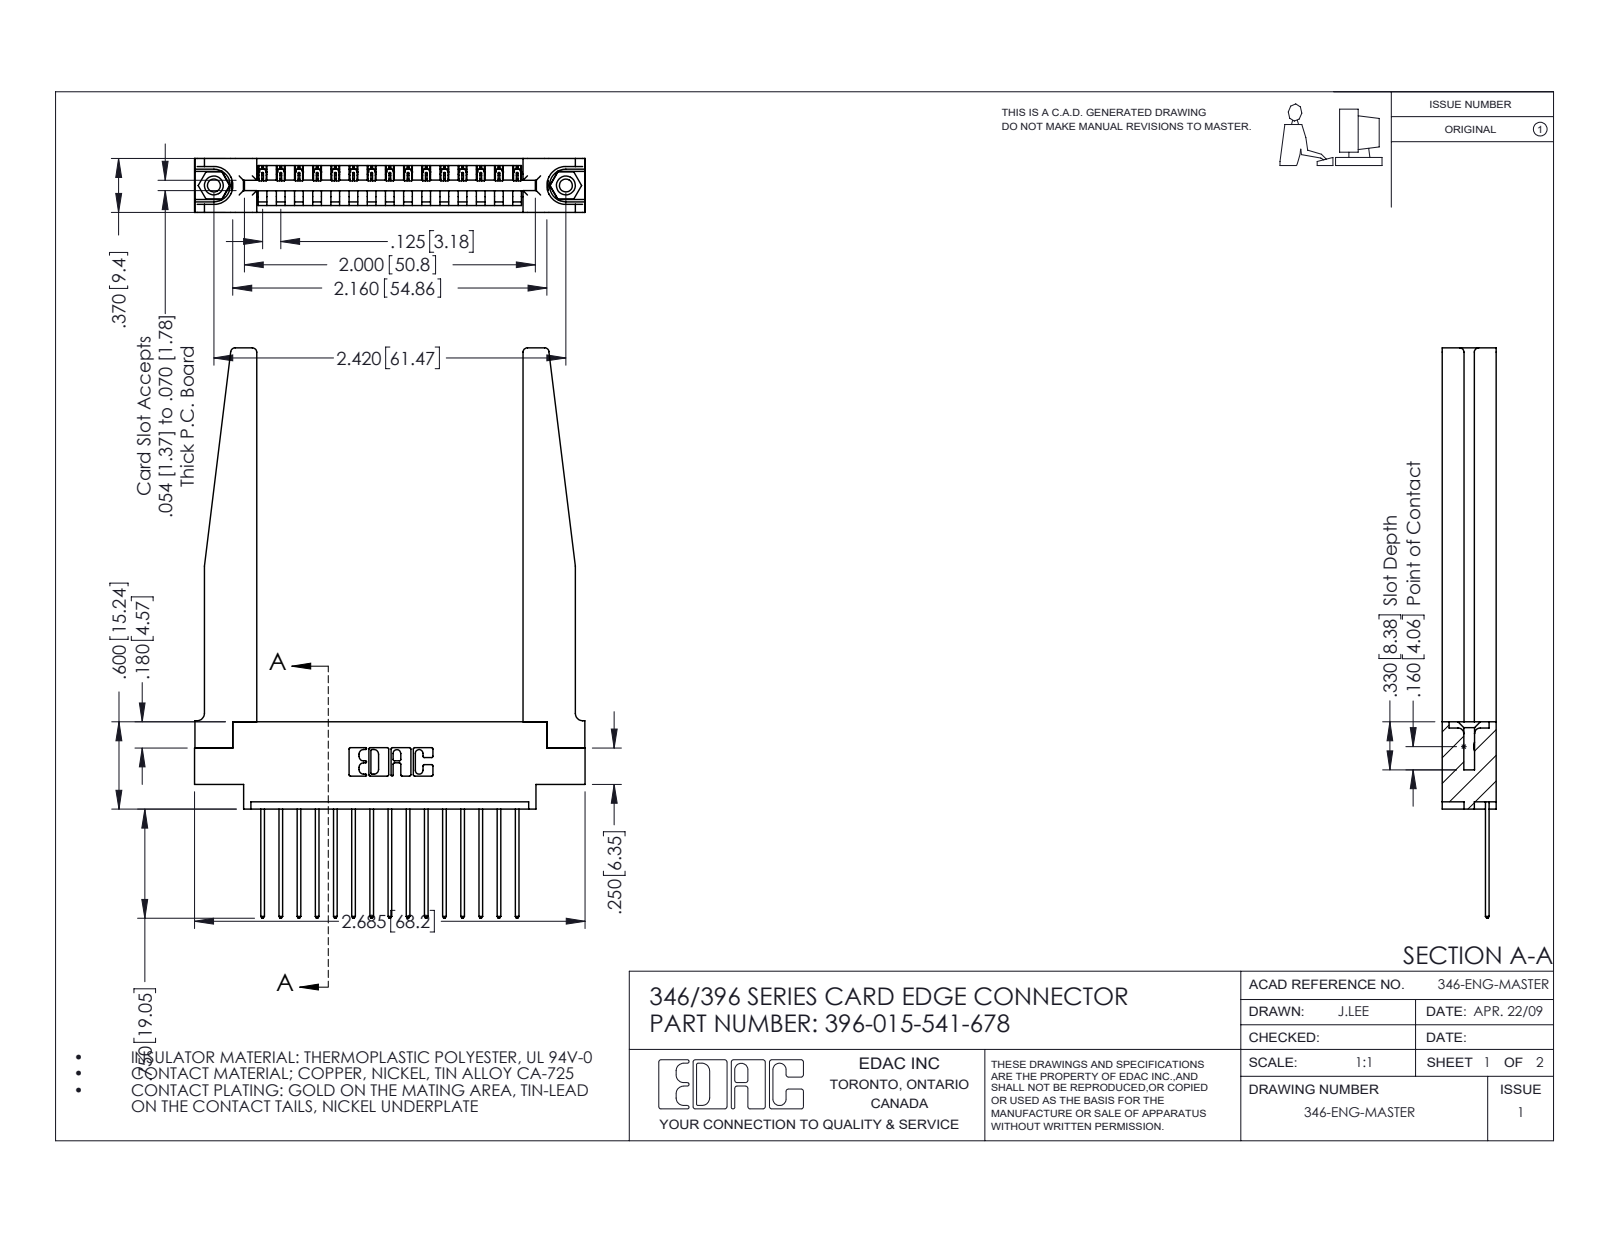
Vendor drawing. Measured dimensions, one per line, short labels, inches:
name: 396-015-541-678; 345-292-001_345-293-141; 346 Part_0.170 Offset - 0.156 Dia-TH; 345-250-001_345-250-001-102 (+1 more)
written by: SolidWorks 2016 (CONFIG_CONTROL_DESIGN)
unit: in
bodies: 20 solids, 1230 faces (822 planar, 356 cylindrical, 52 other)
size: 3.92 × 2.685 × 0.37
volume: 0.802 in³; area: 22.48 in²
holes: 2× ⌀0.089, 2× ⌀0.125, 2× ⌀0.156, 1× ⌀0.064
bosses: 2× ⌀0.155
rounds: 30× R0.006, 30× R0.01, 22× R0.01, 8× R0.03, 6× R0.007, 6× R0.031, 3× R0.026, 2× R0.031
face distances: 0.37, 0.072, 0.048, 0.322, 0.15, 0.148, 0.25, 0.298, 0.025, 0.102
hole spacings: 0.246, 2.213, 2.42
